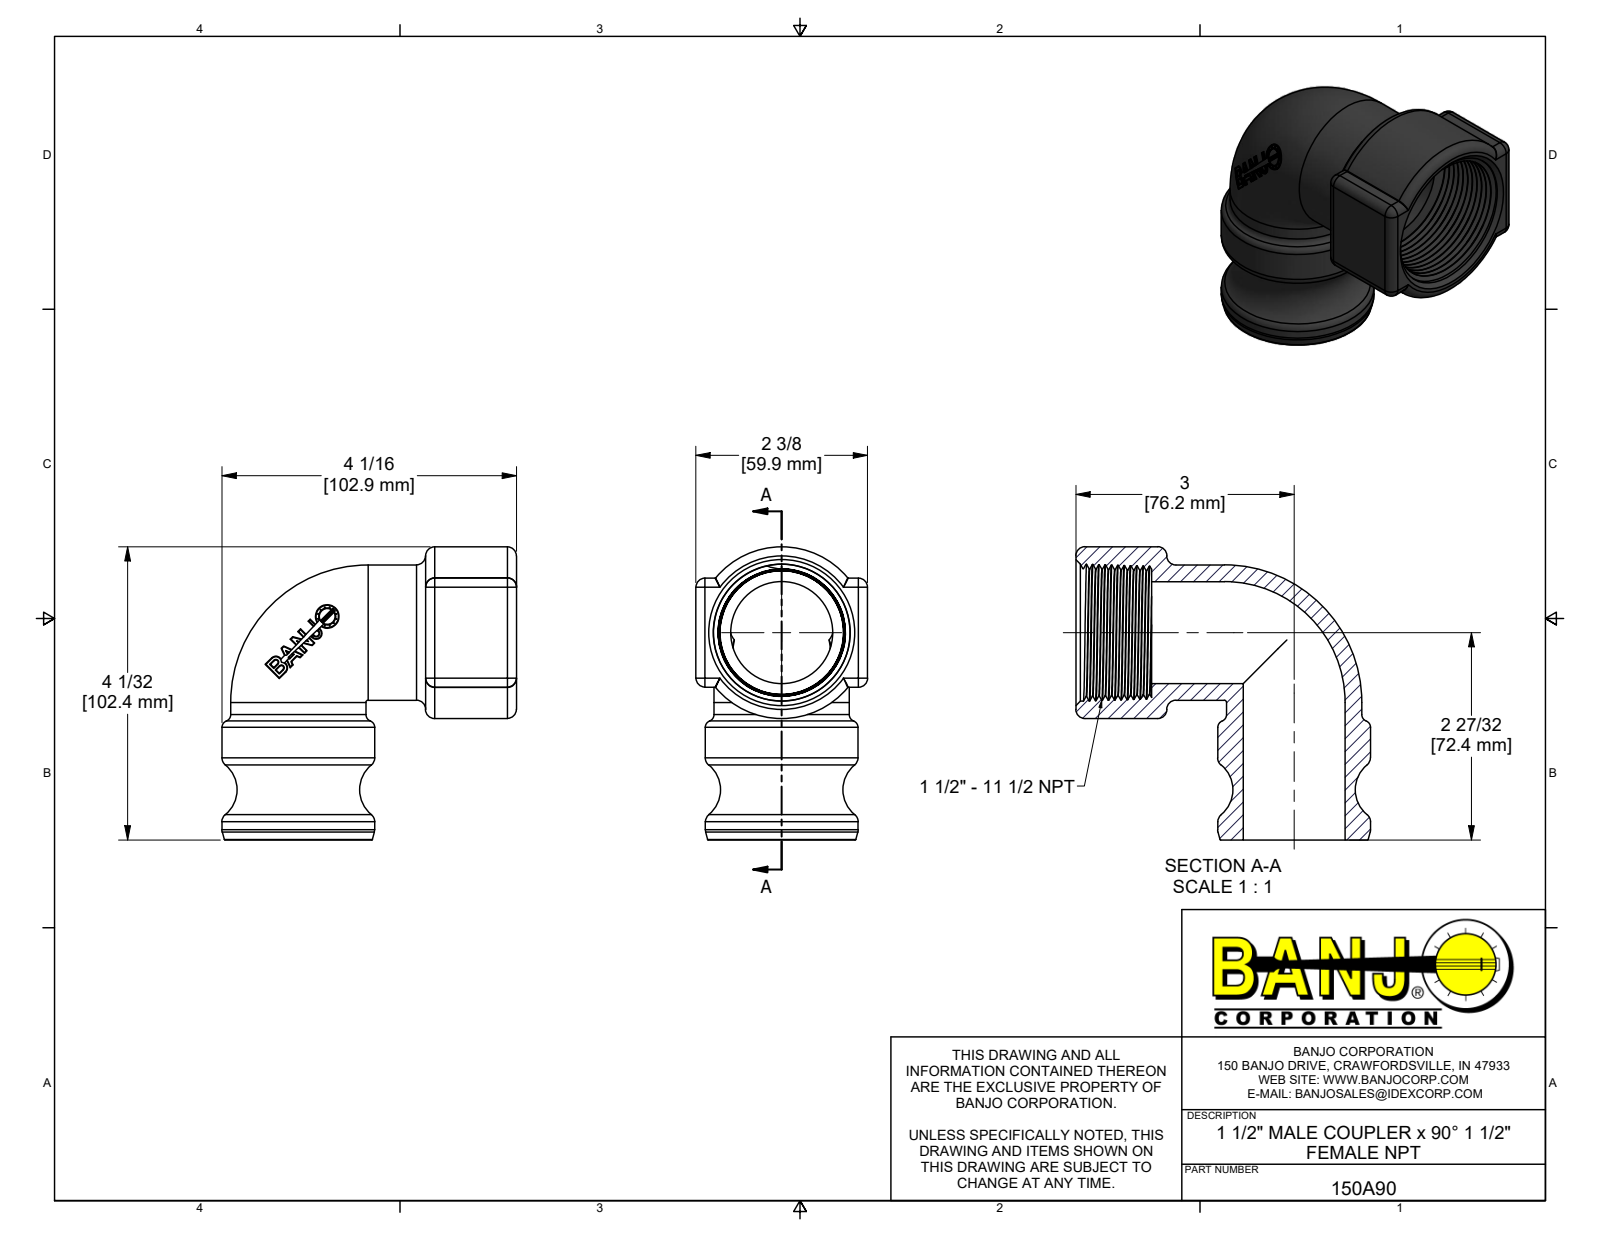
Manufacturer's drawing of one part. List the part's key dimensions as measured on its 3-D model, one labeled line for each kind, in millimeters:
Part name (STEP PRODUCT): 150A90; 150A90U
STEP written by: Autodesk Inventor 2019 (AUTOMOTIVE_DESIGN)
Units: millimetres
Bodies: 1 solid, 411 faces (217 planar, 64 cylindrical, 130 other)
Overall size (bounding box): 770.7 × 102.4 × 59.9
Volume: 135 800 mm³ · Surface area: 156 800 mm²
Round holes (diameter × count): ⌀35.6 ×2, ⌀5.5 ×1, ⌀7.8 ×1
Round bosses / shafts (diameter × count): ⌀47.2 ×2, ⌀53.3 ×1, ⌀8.2 ×1
Partial cylindrical surfaces — rounded edges, fillets, slot ends (radius × count): R3.2 ×12, R0.3 ×4, R0.8 ×2, R1 ×2, R1.9 ×2, R2.1 ×2, R1 ×1, R1.2 ×1
Main face-to-face distances: 59.9, 26.4, 53.3, 91.4, 38.1, 5.3, 31.8, 1.1, 0.3, 2.9
